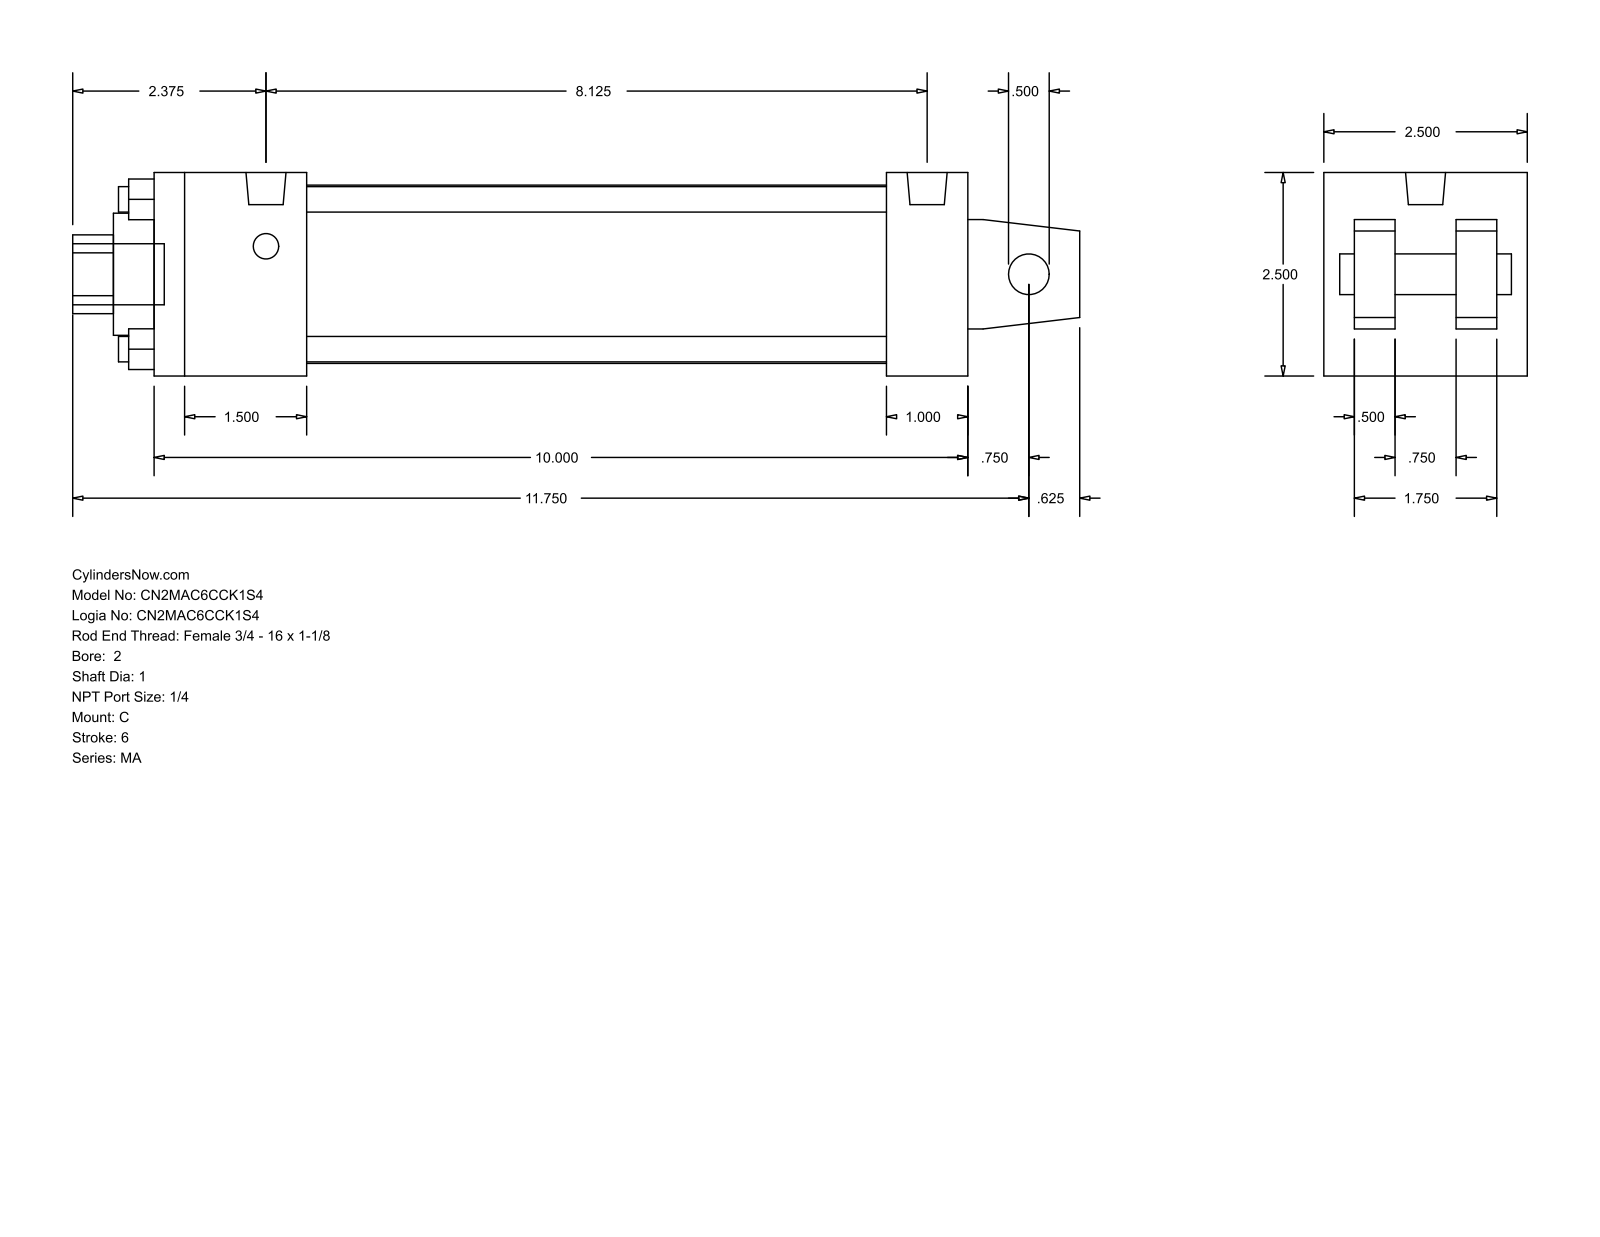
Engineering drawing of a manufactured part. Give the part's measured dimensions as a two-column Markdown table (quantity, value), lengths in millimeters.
| quantity | value |
| --- | --- |
| part name | MA_C__0200_1 |
| STEP written by | GSSL Pune (CONFIG_CONTROL_DESIGN) |
| units | millimeters |
| bodies | 0 solids, 103 faces (76 planar, 27 cylindrical, 0 other) |
| overall size | 314.32 × 63.5 × 63.5 |
| round holes (diameter × count) | 7.94 × 4, 12.7 × 1, 25.4 × 1, 38.1 × 1, 55.63 × 1 |
| round bosses / shafts (diameter × count) | 7.94 × 4, 12.49 × 2, 19.05 × 1 |
| partial cylindrical surfaces (radius × count) | 12.29 × 1 |
| main face-to-face distances | 63.5, 12.7, 254, 22.22, 41.28, 9.52, 53.98, 31.76, 47.63, 25.4 |
| hole center spacings | 33.05, 46.74, 66.1 |
